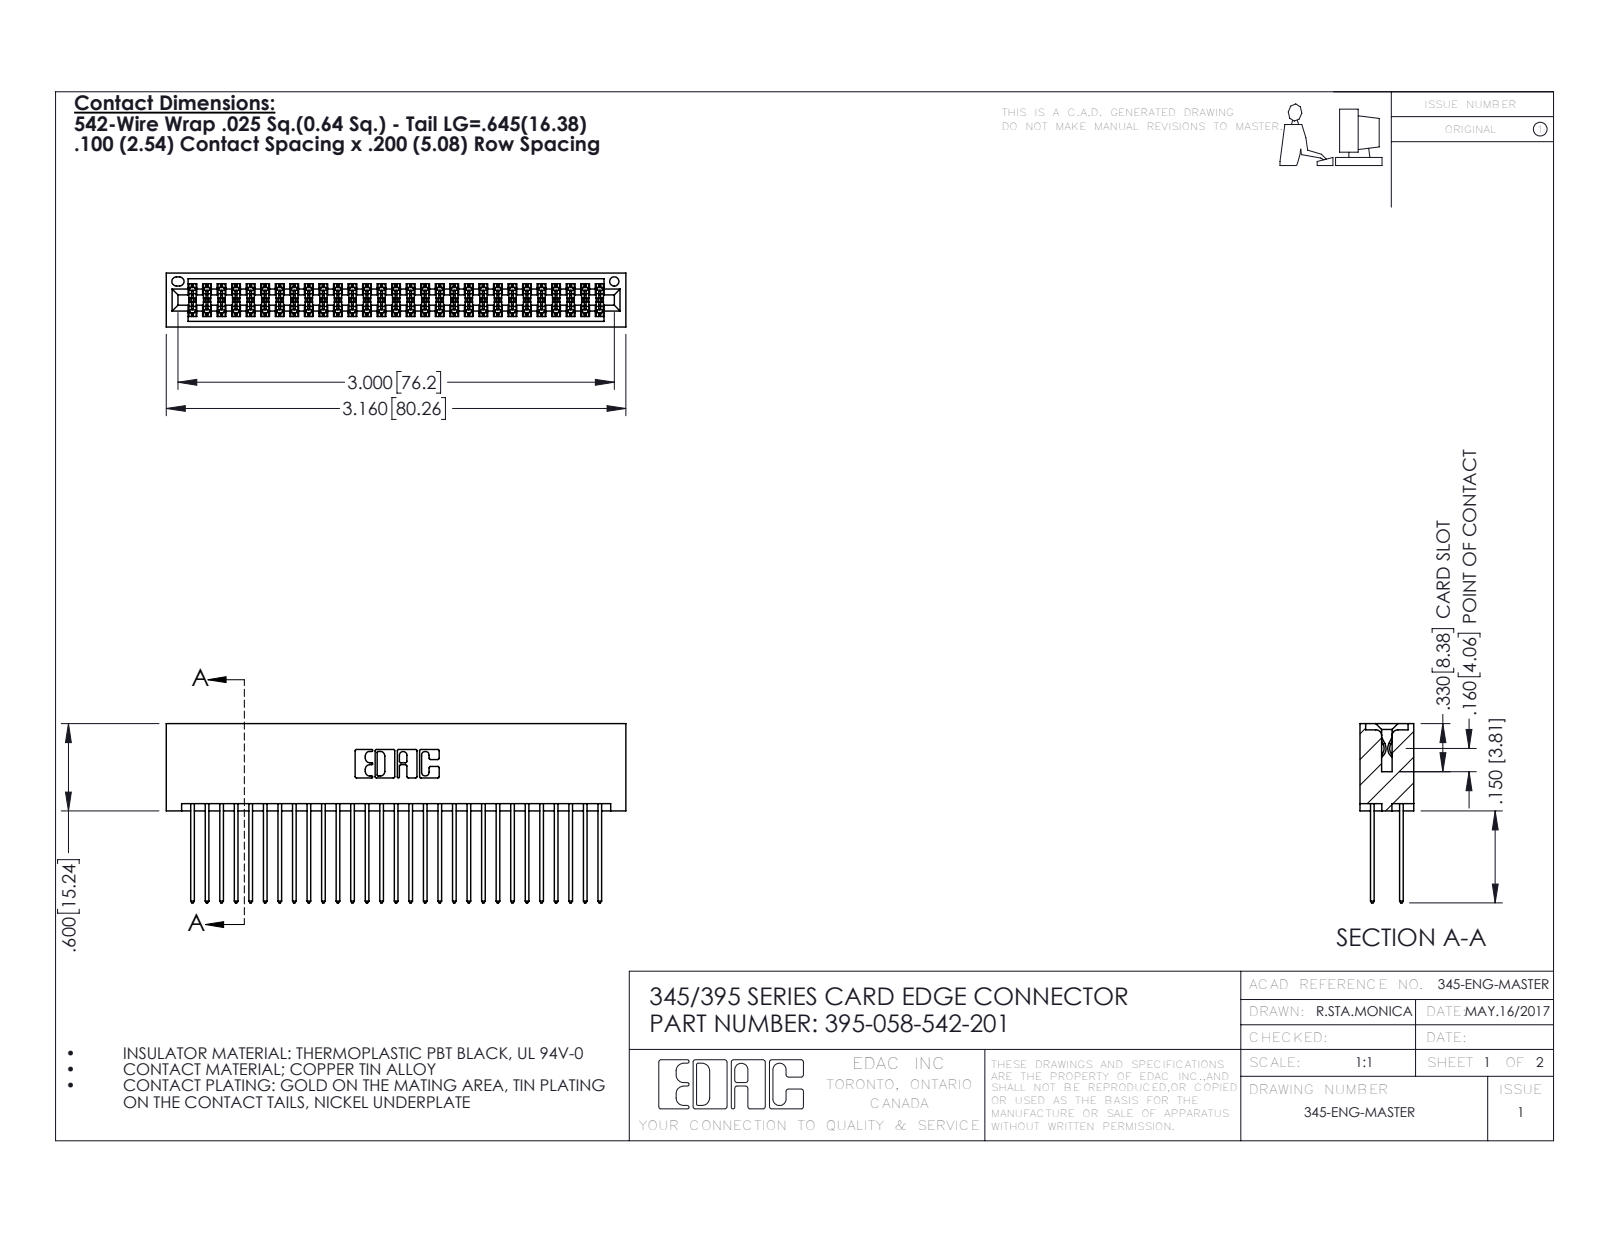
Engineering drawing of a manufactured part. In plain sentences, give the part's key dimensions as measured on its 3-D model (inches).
The part is named "395-058-542-201; 345 Part_No Mounting Lugs; 345-292-001_345-293-142". Its 3-D file was written by "SolidWorks 2016 (CONFIG_CONTROL_DESIGN)". It is 59 solids with 3018 faces: 1990 planar, 1028 cylindrical and 0 other. Overall it measures 3.16 by 1.232 by 0.37 inches. Its volume is 0.523 cubic inches and its surface area 21.66 square inches. Round holes: 1 of diameter 0.064. Partial cylindrical surfaces (rounded edges, fillets, slot ends): 87 of radius 0.006, 58 of radius 0.01, 22 of radius 0.01, 6 of radius 0.007, 6 of radius 0.031, 3 of radius 0.026, 2 of radius 0.014, 2 of radius 0.019. The main face-to-face distances are 0.298, 0.072, 0.2, 0.098, 0.272, 0.025, 0.225, 0.37, 0.175, 0.149.
